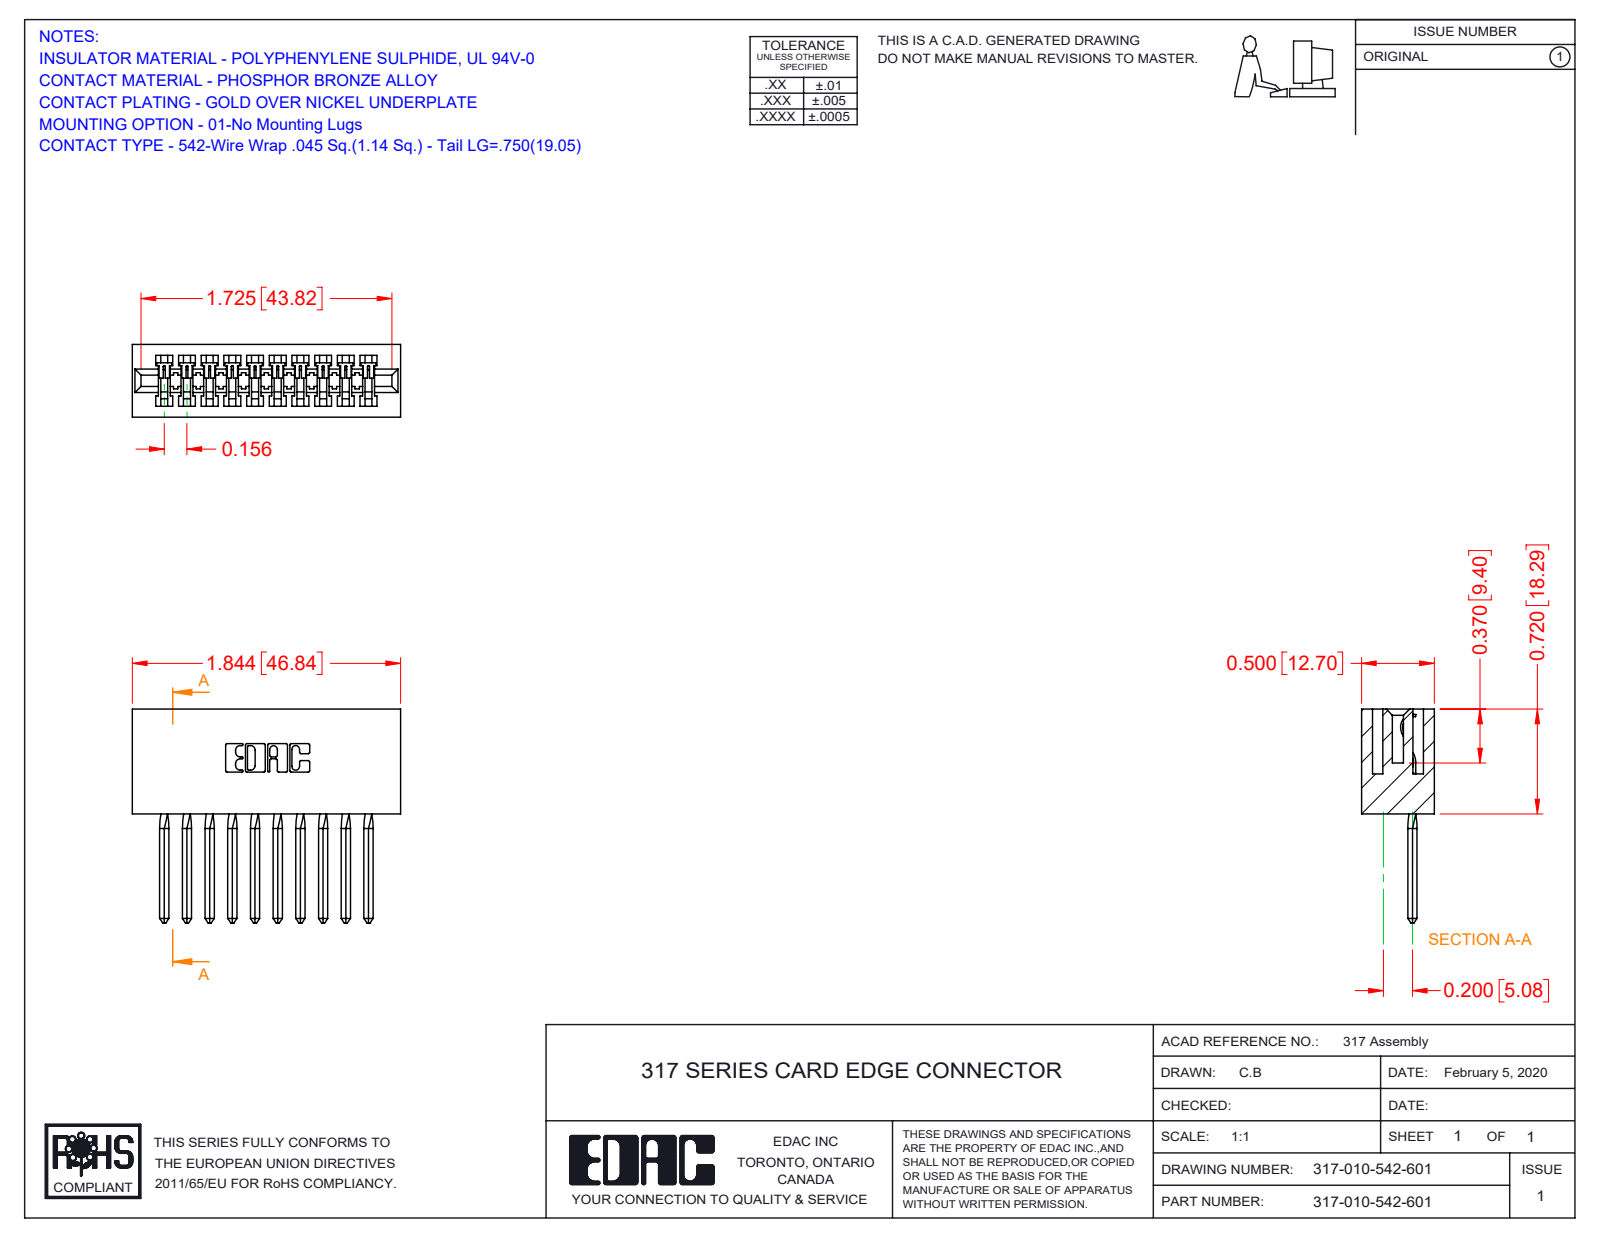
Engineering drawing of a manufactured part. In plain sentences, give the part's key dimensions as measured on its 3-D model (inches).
The part is named "317-290-003_542; 317-010-542-601; 317 Part_Lugless". Its 3-D file was written by "SolidWorks 2016 (CONFIG_CONTROL_DESIGN)". It is 11 solids with 840 faces: 690 planar, 110 cylindrical and 40 other. Overall it measures 1.844 by 1.47 by 0.5 inches. Its volume is 0.486 cubic inches and its surface area 14.02 square inches. Partial cylindrical surfaces (rounded edges, fillets, slot ends): 22 of radius 0.01, 20 of radius 0.006, 6 of radius 0.007, 6 of radius 0.031, 3 of radius 0.026, 1 of radius 0.074, 1 of radius 0.089, 1 of radius 0.1. The main face-to-face distances are 0.5, 0.075, 0.425, 0.11, 0.065, 0.156, 0.22, 0.624, 0.116, 0.35.
